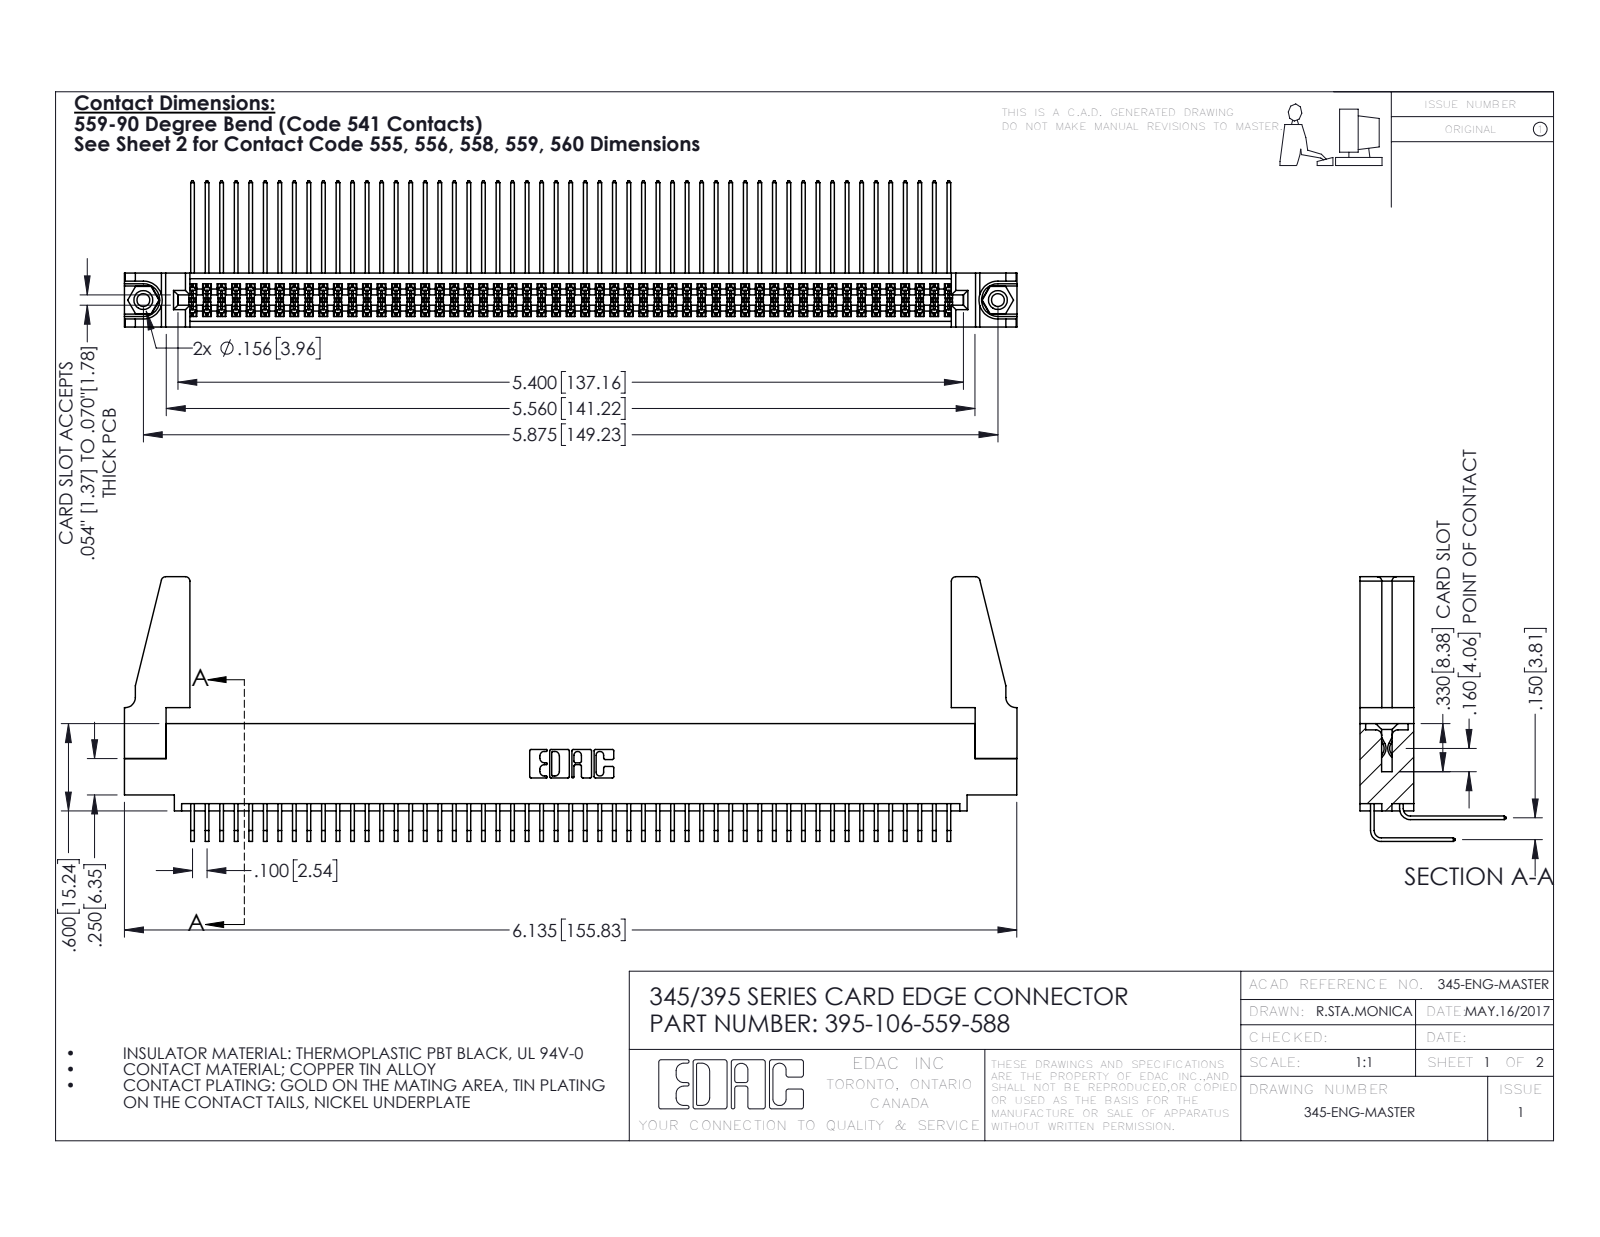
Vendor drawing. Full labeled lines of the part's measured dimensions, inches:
Part name (STEP PRODUCT): 345 Part_0.110 Offset - 0.156 Dia-TH; 395-106-559-588; 345-220-078_345-220-088; 345-292-001_559 Tail - 2 (+2 more)
STEP written by: SolidWorks 2016 (CONFIG_CONTROL_DESIGN)
Units: inches
Bodies: 111 solids, 5766 faces (3866 planar, 1884 cylindrical, 16 other)
Overall size (bounding box): 6.136 × 1.819 × 1.005
Volume: 1.161 in³ · Surface area: 45.93 in²
Round holes (diameter × count): ⌀0.089 ×2, ⌀0.125 ×2, ⌀0.156 ×2, ⌀0.064 ×1
Round bosses / shafts (diameter × count): ⌀0.155 ×2
Partial cylindrical surfaces — rounded edges, fillets, slot ends (radius × count): R0.006 ×159, R0.01 ×22, R0.03 ×8, R0.007 ×6, R0.031 ×6, R0.026 ×3, R0.014 ×2, R0.019 ×2
Main face-to-face distances: 0.072, 0.298, 0.37, 0.2, 0.098, 0.272, 0.025, 0.225, 0.175, 0.15
Hole centre spacings: 0.27, 5.639, 5.875
